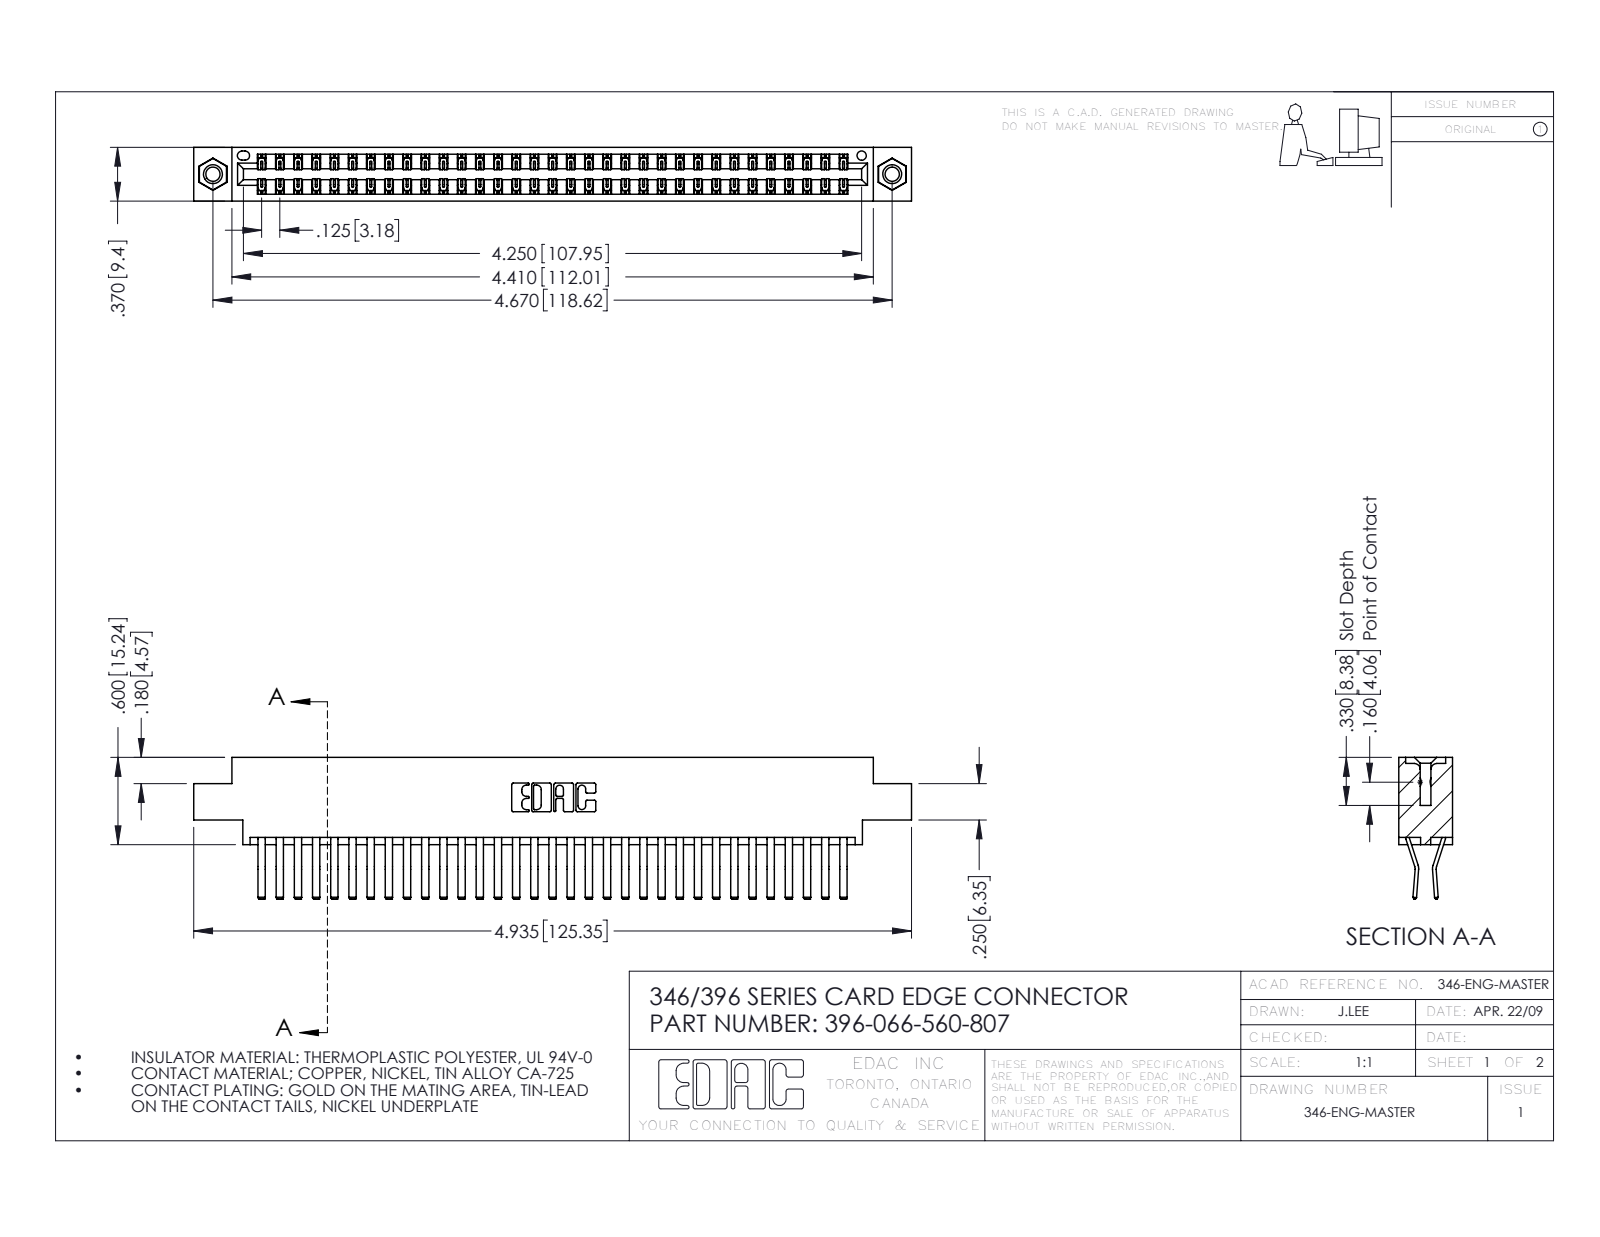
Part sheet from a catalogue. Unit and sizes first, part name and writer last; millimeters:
Units: millimetres
Overall size (bounding box): 125.3 × 24.8 × 9.4
Round holes (diameter × count): ⌀2.5 ×2, ⌀3.2 ×2, ⌀4 ×2, ⌀1.6 ×1
Round bosses / shafts (diameter × count): ⌀3.9 ×2
Partial cylindrical surfaces — rounded edges, fillets, slot ends (radius × count): R0.2 ×99, R0.3 ×22, R0.2 ×6, R0.8 ×6, R0.7 ×3, R0.3 ×2, R0.4 ×2, R0.6 ×2
Main face-to-face distances: 1.2, 8.2, 9.4, 0.6, 6.4, 1.8, 7.6, 7, 5.6, 3.8
Hole centre spacings: 6.2, 113.3, 118.6
Volume: 12 400 mm³ · Surface area: 18 300 mm²
Bodies: 69 solids, 3750 faces (2422 planar, 1312 cylindrical, 16 other)
Part name (STEP PRODUCT): 345-292-001_560 Tail; 345-250-001_345-250-005-103; 346 Part_0.170 Offset - 0.156 Dia-TI; 396-066-560-807
STEP written by: SolidWorks 2016 (CONFIG_CONTROL_DESIGN)
